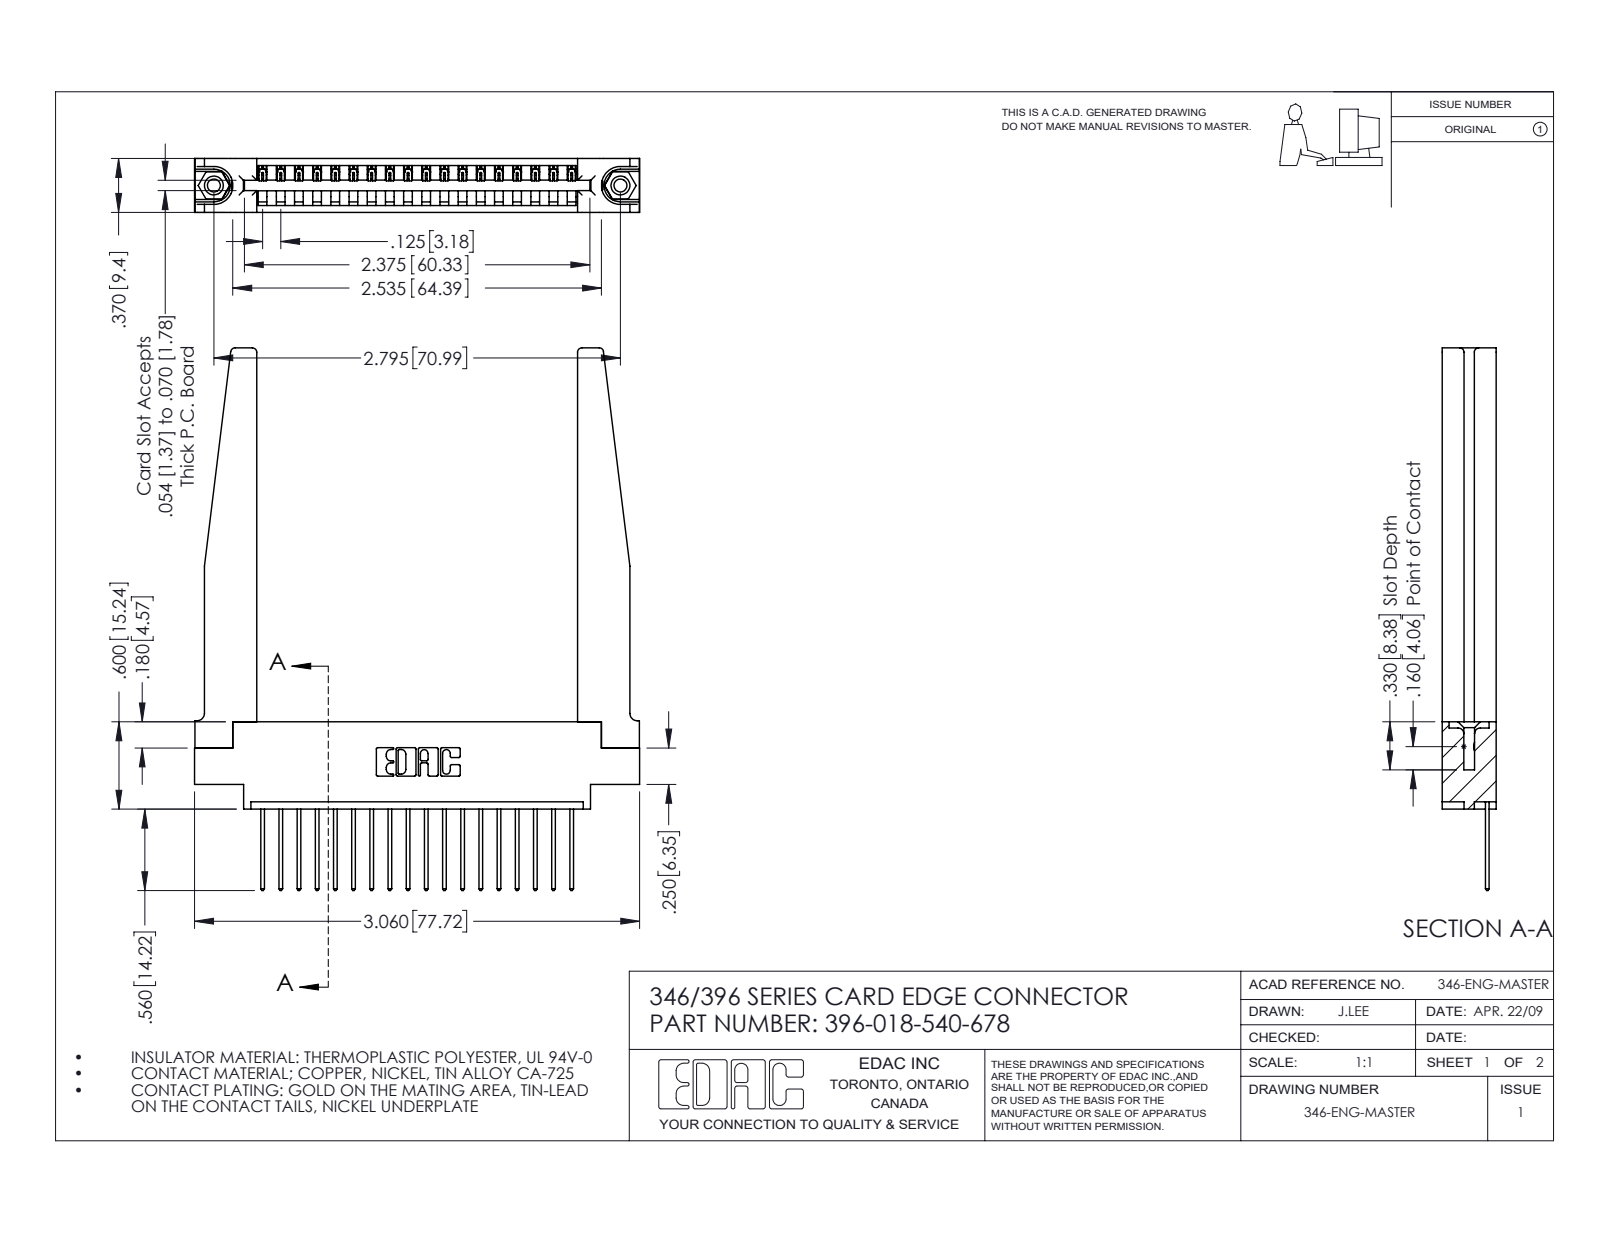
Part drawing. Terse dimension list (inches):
name: 346 Part_0.170 Offset - 0.156 Dia-TH; 396-018-540-678; 345-292-001_345-293-140; 345-250-001_345-250-001-102 (+1 more)
written by: SolidWorks 2016 (CONFIG_CONTROL_DESIGN)
unit: in
bodies: 23 solids, 1404 faces (942 planar, 410 cylindrical, 52 other)
size: 3.73 × 3.06 × 0.37
volume: 0.858 in³; area: 24.1 in²
holes: 2× ⌀0.089, 2× ⌀0.125, 2× ⌀0.156, 1× ⌀0.064
bosses: 2× ⌀0.155
rounds: 36× R0.006, 36× R0.01, 22× R0.01, 8× R0.03, 6× R0.007, 6× R0.031, 3× R0.026, 2× R0.031
face distances: 0.37, 0.072, 0.048, 0.322, 0.15, 0.148, 0.25, 0.298, 0.025, 0.102
hole spacings: 0.246, 2.588, 2.795
